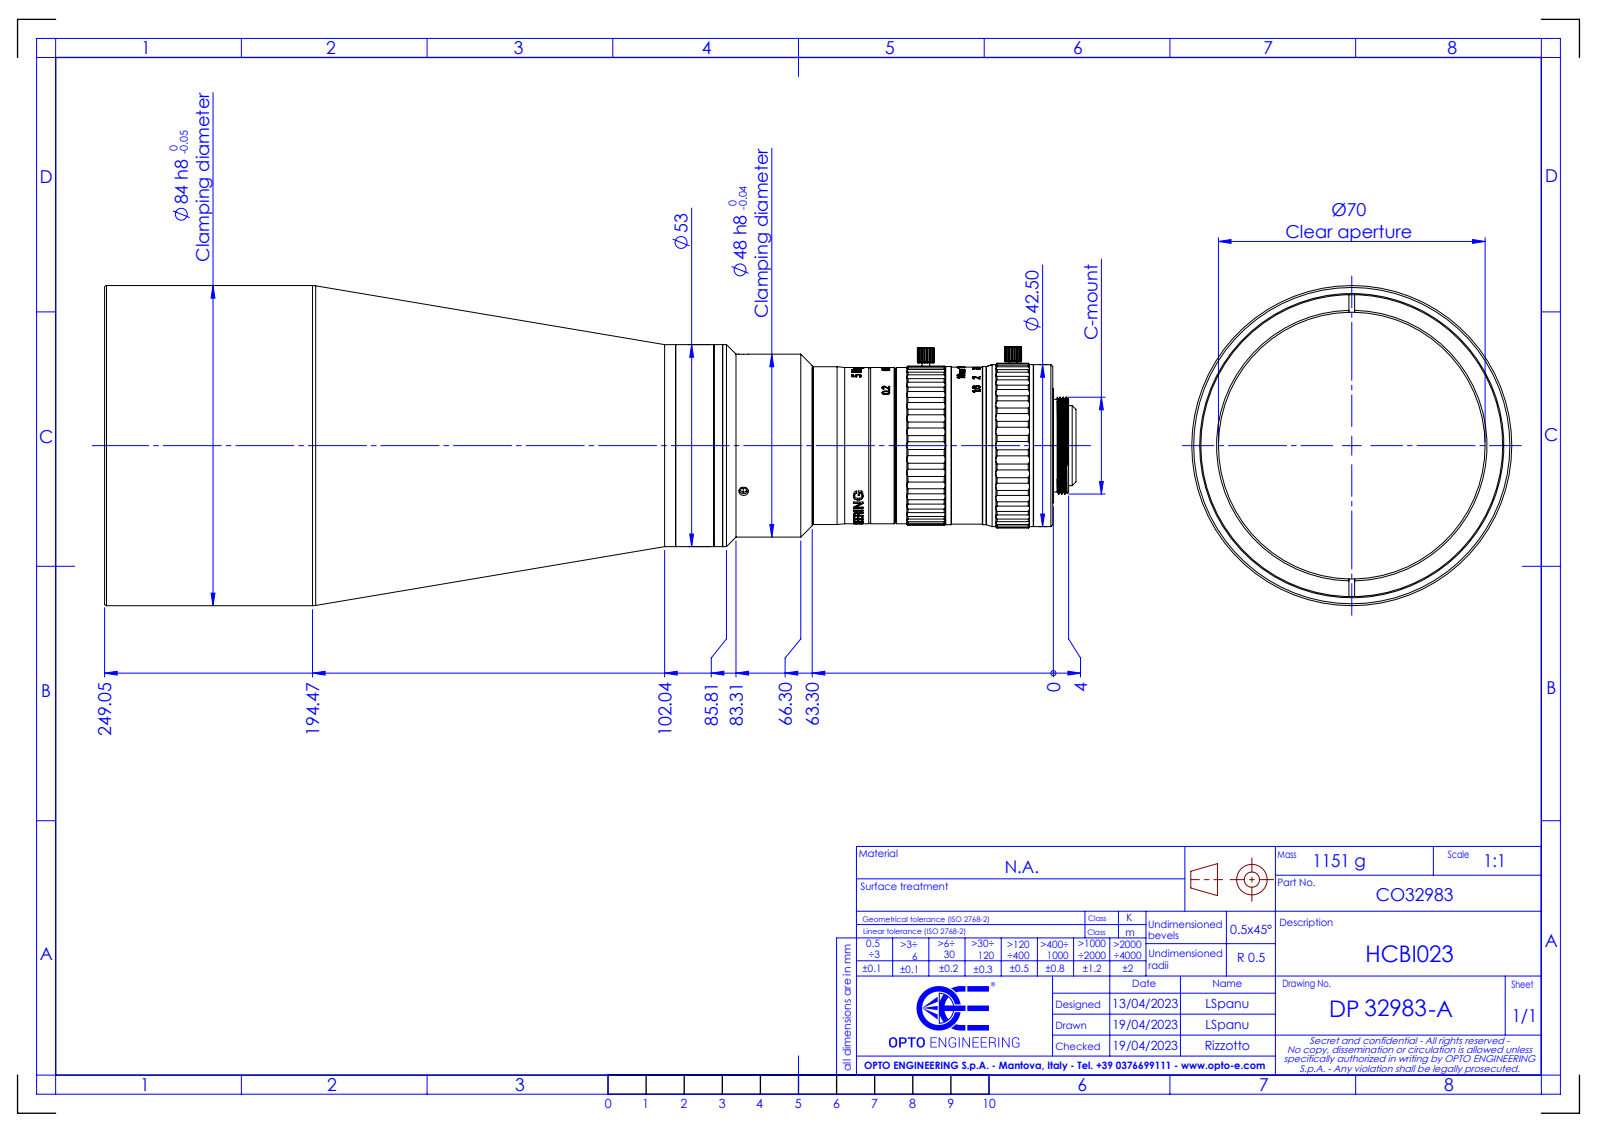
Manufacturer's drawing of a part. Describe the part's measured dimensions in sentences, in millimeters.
The part is named "DP32983-A_HCBI023". Its 3-D file was written by "SolidWorks 2021 (CONFIG_CONTROL_DESIGN)". It is 0 solids with 601 faces: 77 planar, 355 cylindrical and 169 other. Overall it measures 254.99 by 84 by 84 millimeters. Round holes: 3 of diameter 2.5, 1 of diameter 70, 1 of diameter 79.25. Round bosses or shafts: 1 of diameter 84, 1 of diameter 53, 1 of diameter 48, 1 of diameter 42.5, 1 of diameter 41.5, 1 of diameter 41.4, 1 of diameter 41.2, 1 of diameter 41. Partial cylindrical surfaces (rounded edges, fillets, slot ends): 72 of radius 2, 2 of radius 1.3, 2 of radius 2.25, 1 of radius 20.45, 1 of radius 20.55, 1 of radius 20.9, 1 of radius 21.65. The main face-to-face distances are 2.75, 161.73, 158.98, 248.39, 245.64, 86.66, 159.5, 156.75, 2.23, 88.89.
